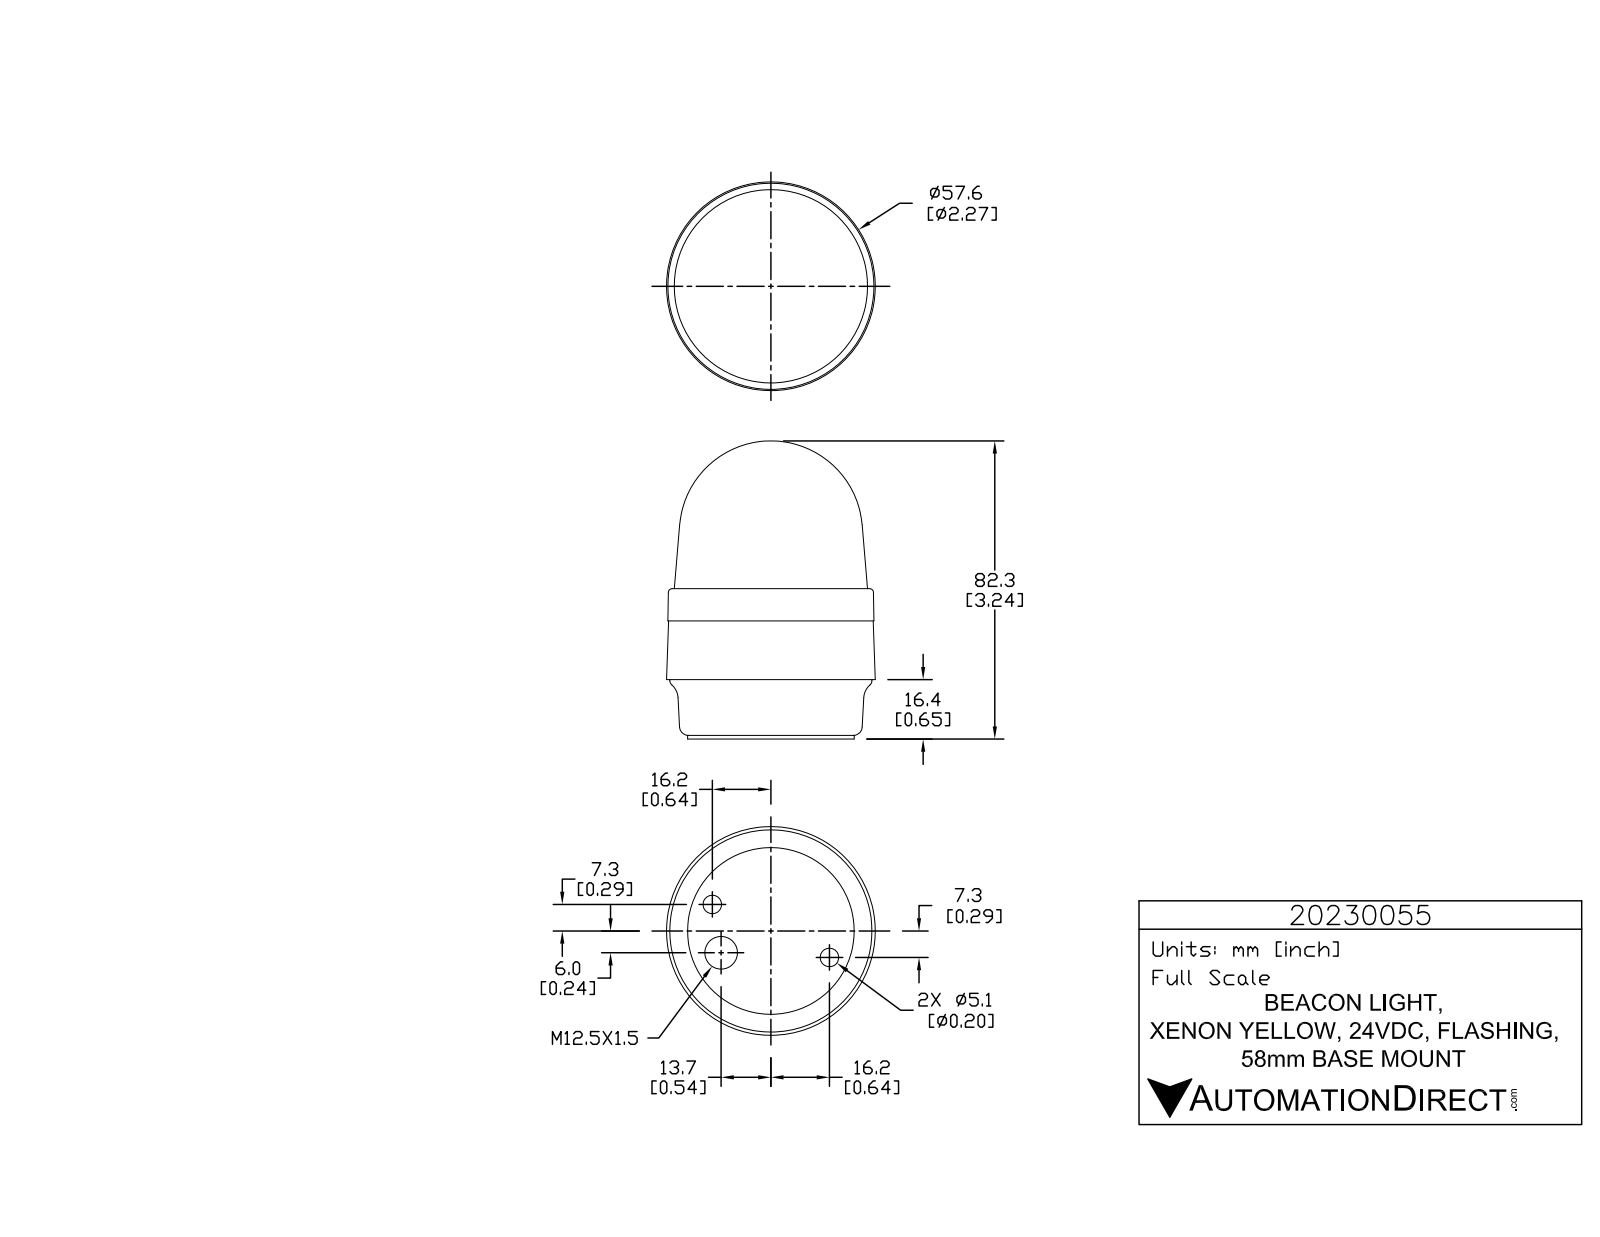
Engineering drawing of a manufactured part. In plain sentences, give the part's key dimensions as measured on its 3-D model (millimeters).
The part is named "20230055". Its 3-D file was written by "SolidWorks 2015 (AUTOMOTIVE_DESIGN)". It is 1 solid with 763 faces: 527 planar, 145 cylindrical and 91 other. Overall it measures 82.3 by 57.63 by 57.63 millimeters. Its volume is 164 395 cubic millimeters and its surface area 16 261 square millimeters. Round holes: 3 of diameter 0.99, 2 of diameter 5.11, 1 of diameter 9. Round bosses or shafts: 3 of diameter 5.74, 3 of diameter 1.43, 1 of diameter 55.8, 1 of diameter 46. Partial cylindrical surfaces (rounded edges, fillets, slot ends): 6 of radius 0.2, 6 of radius 0.21, 6 of radius 0.21, 6 of radius 3.32, 3 of radius 0.1, 3 of radius 0.12, 3 of radius 0.19, 3 of radius 0.2. The main face-to-face distances are 16.4, 1, 15.4, 41.5, 40.5, 25.1, 32.6, 31.6, 16.2, 8.9. The hole center spacings are 13.56, 29.94, 35.5.
